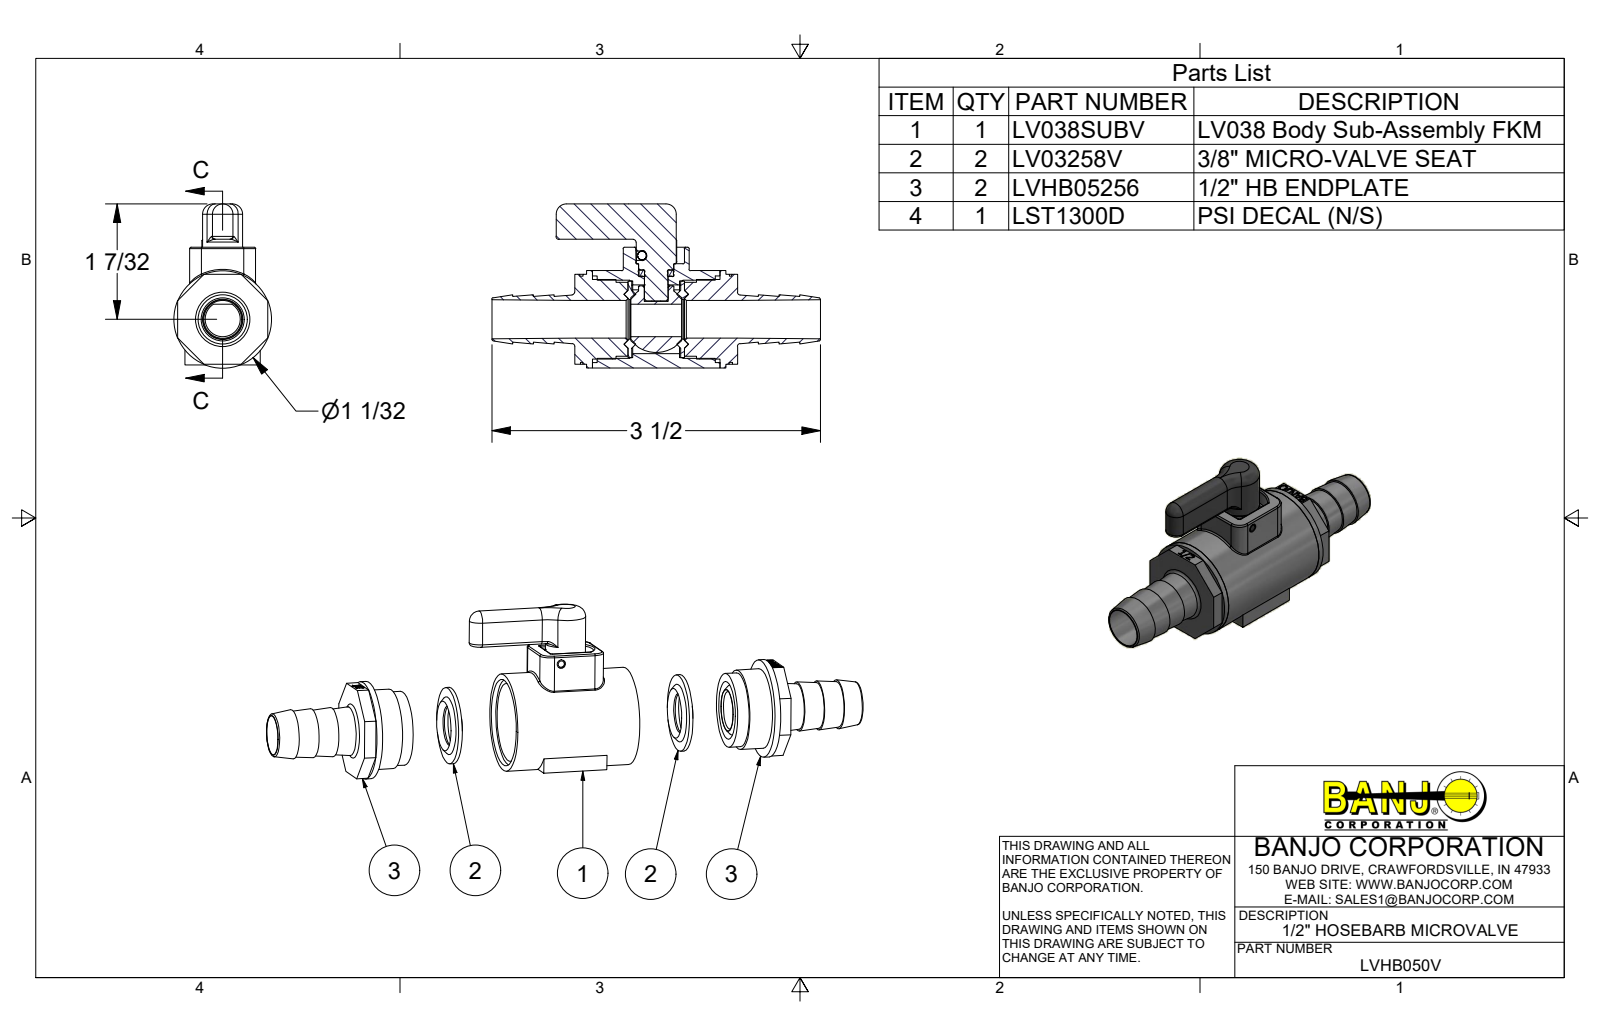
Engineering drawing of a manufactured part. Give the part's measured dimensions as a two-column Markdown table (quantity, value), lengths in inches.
| quantity | value |
| --- | --- |
| part name | LVHB050V; LV038SUBV; LV03254A; AQ010V (+5 more) |
| STEP written by | Autodesk Inventor 2012 (AUTOMOTIVE_DESIGN) |
| units | inches |
| bodies | 9 solids, 647 faces (292 planar, 103 cylindrical, 252 other) |
| overall size | 3.49 × 1.743 × 1.035 |
| volume | 1.549 in³ |
| surface area | 29.82 in² |
| round holes (diameter × count) | 0.093 × 1, 0.251 × 1, 0.368 × 1, 0.37 × 1, 0.376 × 1, 0.4 × 1, 0.421 × 1, 0.73 × 1, 0.815 × 1, 0.83 × 1, 0.92 × 1 |
| round bosses / shafts (diameter × count) | 1.035 × 1, 0.845 × 1, 0.812 × 1, 0.785 × 1, 0.425 × 1, 0.375 × 1, 0.372 × 1, 0.25 × 1 |
| partial cylindrical surfaces (radius × count) | 0.01 × 16, 0.015 × 14, 0.125 × 4, 0.03 × 2, 0.05 × 2, 0.109 × 2, 0.25 × 2, 0.048 × 1 |
| main face-to-face distances | 0.977, 0.188, 1.542, 0.565, 1.165, 0.377, 0.05, 0.327, 1.73, 1.354 |
